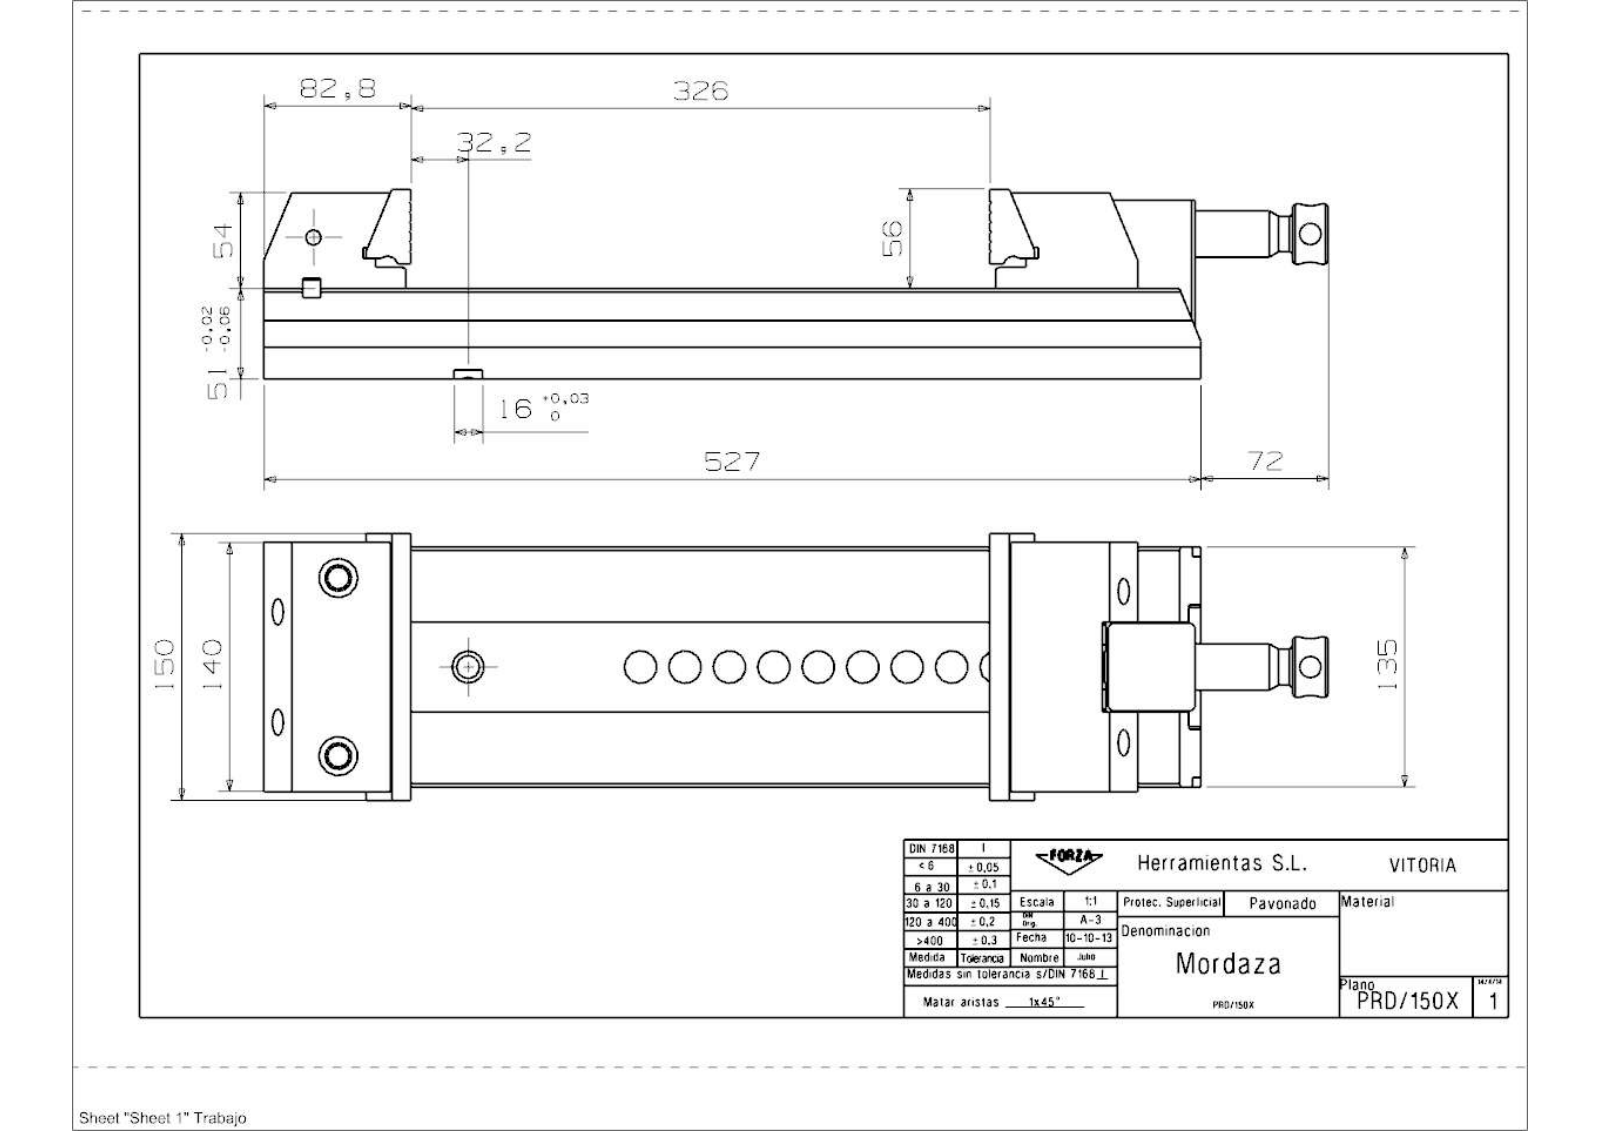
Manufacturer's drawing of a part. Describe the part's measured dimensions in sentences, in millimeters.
The part is named "30_150X_Mordaza". Its 3-D file was written by "SIEMENS PLM Software NX 7.5 (CONFIG_CONTROL_DESIGN)". It is 12 solids with 438 faces: 283 planar, 98 cylindrical and 57 other. Overall it measures 612.76 by 150 by 107 millimeters. Its volume is 3 767 000 cubic millimeters and its surface area 511 223 square millimeters. Round holes: 6 of diameter 13, 6 of diameter 15, 5 of diameter 5.19, 4 of diameter 6.99, 4 of diameter 8.5, 4 of diameter 8.78, 4 of diameter 10, 4 of diameter 10.58, 4 of diameter 19, 2 of diameter 12, 2 of diameter 12.38, 2 of diameter 18. Round bosses or shafts: 1 of diameter 34, 1 of diameter 33.8, 1 of diameter 26, 1 of diameter 20, 1 of diameter 16.5. Partial cylindrical surfaces (rounded edges, fillets, slot ends): 4 of radius 1.5, 4 of radius 8, 4 of radius 20, 2 of radius 1.6, 2 of radius 5.5, 2 of radius 6, 1 of radius 4, 1 of radius 9. The main face-to-face distances are 51, 19.3, 31.7, 49.4, 105, 1.6, 17.7, 27, 5.5, 135. The hole center spacings are 11.5, 73.5, 85, 95.17, 95.18, 1, 11.54, 11.61.
